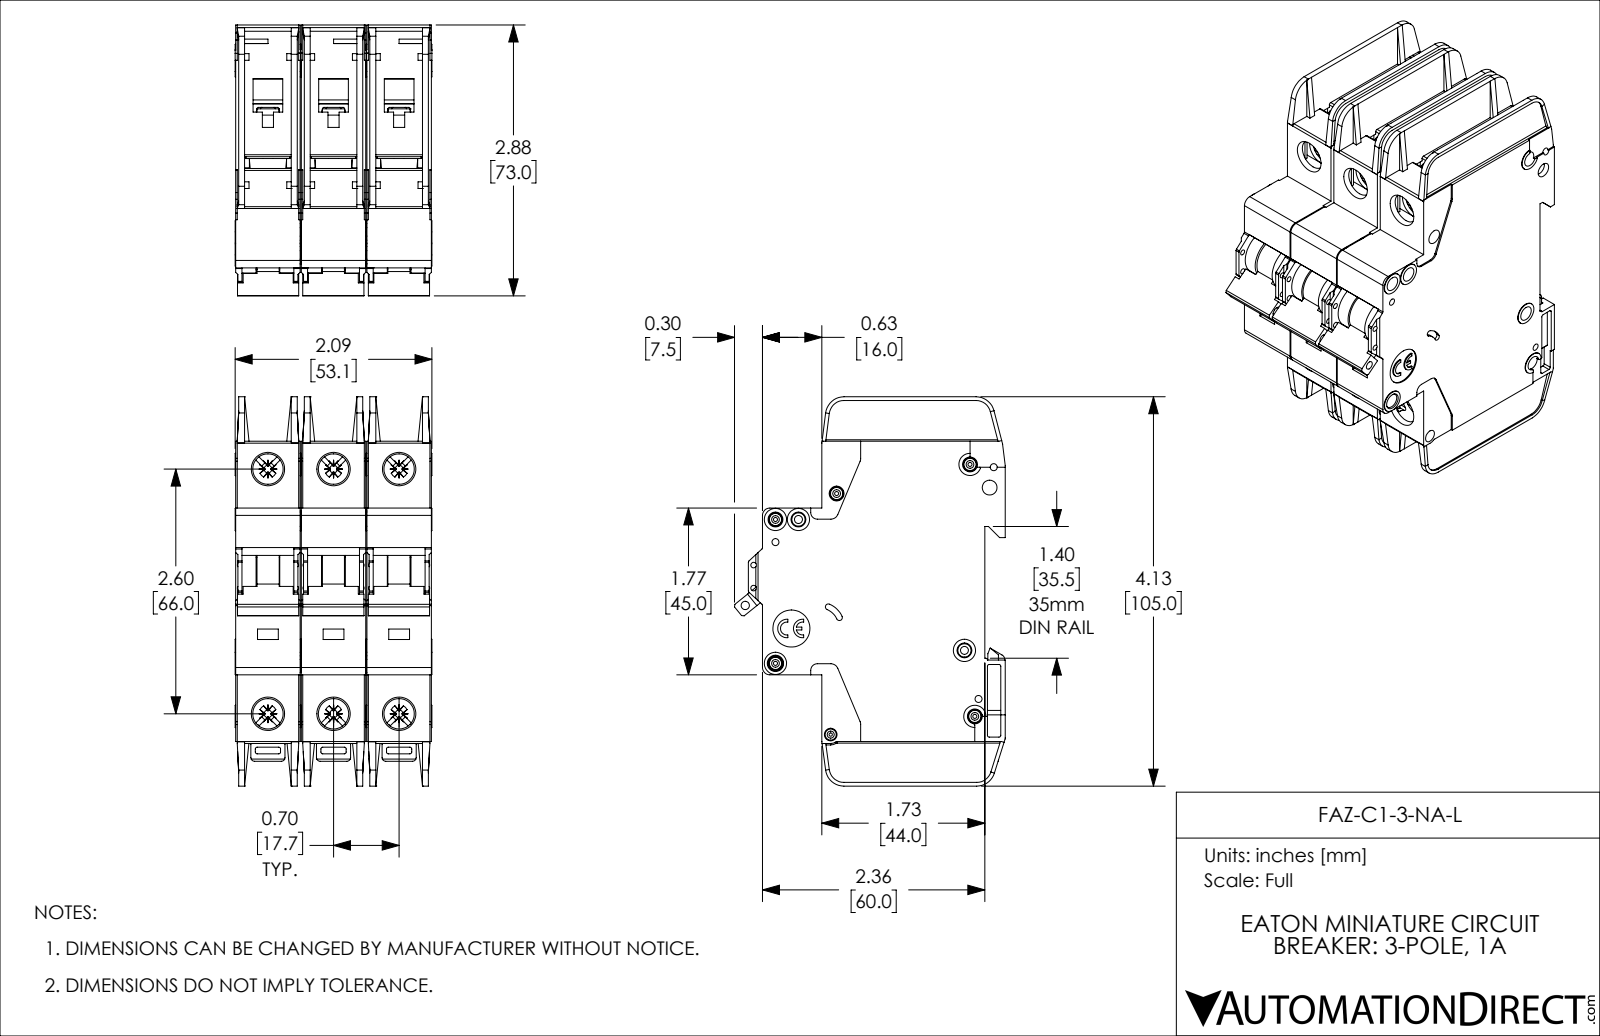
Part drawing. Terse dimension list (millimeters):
name: FAZ-C1-3-NA-L
written by: SolidWorks 2019 (AUTOMOTIVE_DESIGN)
unit: mm
bodies: 3 solids, 3381 faces (2013 planar, 1071 cylindrical, 297 other)
size: 105 × 73.1 × 53.1
volume: 230 200 mm³; area: 79 350 mm²
holes: 8× ⌀4, 6× ⌀8.2, 5× ⌀1.1, 4× ⌀1.9, 2× ⌀1.5, 2× ⌀2.2, 1× ⌀0.9, 1× ⌀2.3, 1× ⌀2.5, 1× ⌀3.4, 1× ⌀10
bosses: 5× ⌀3.3, 4× ⌀6, 4× ⌀3, 3× ⌀2.5
rounds: 72× R0.5, 30× R0.4, 18× R1, 12× R1.1, 12× R2, 6× R0.2, 6× R0.3, 6× R0.7
face distances: 17.7, 1.2, 35.4, 17.4, 15, 35.1, 18.9, 16.5, 2.7, 2.4
hole spacings: 17.7, 68.3, 66, 6.2, 13.6, 22.1, 35.4, 74.9
